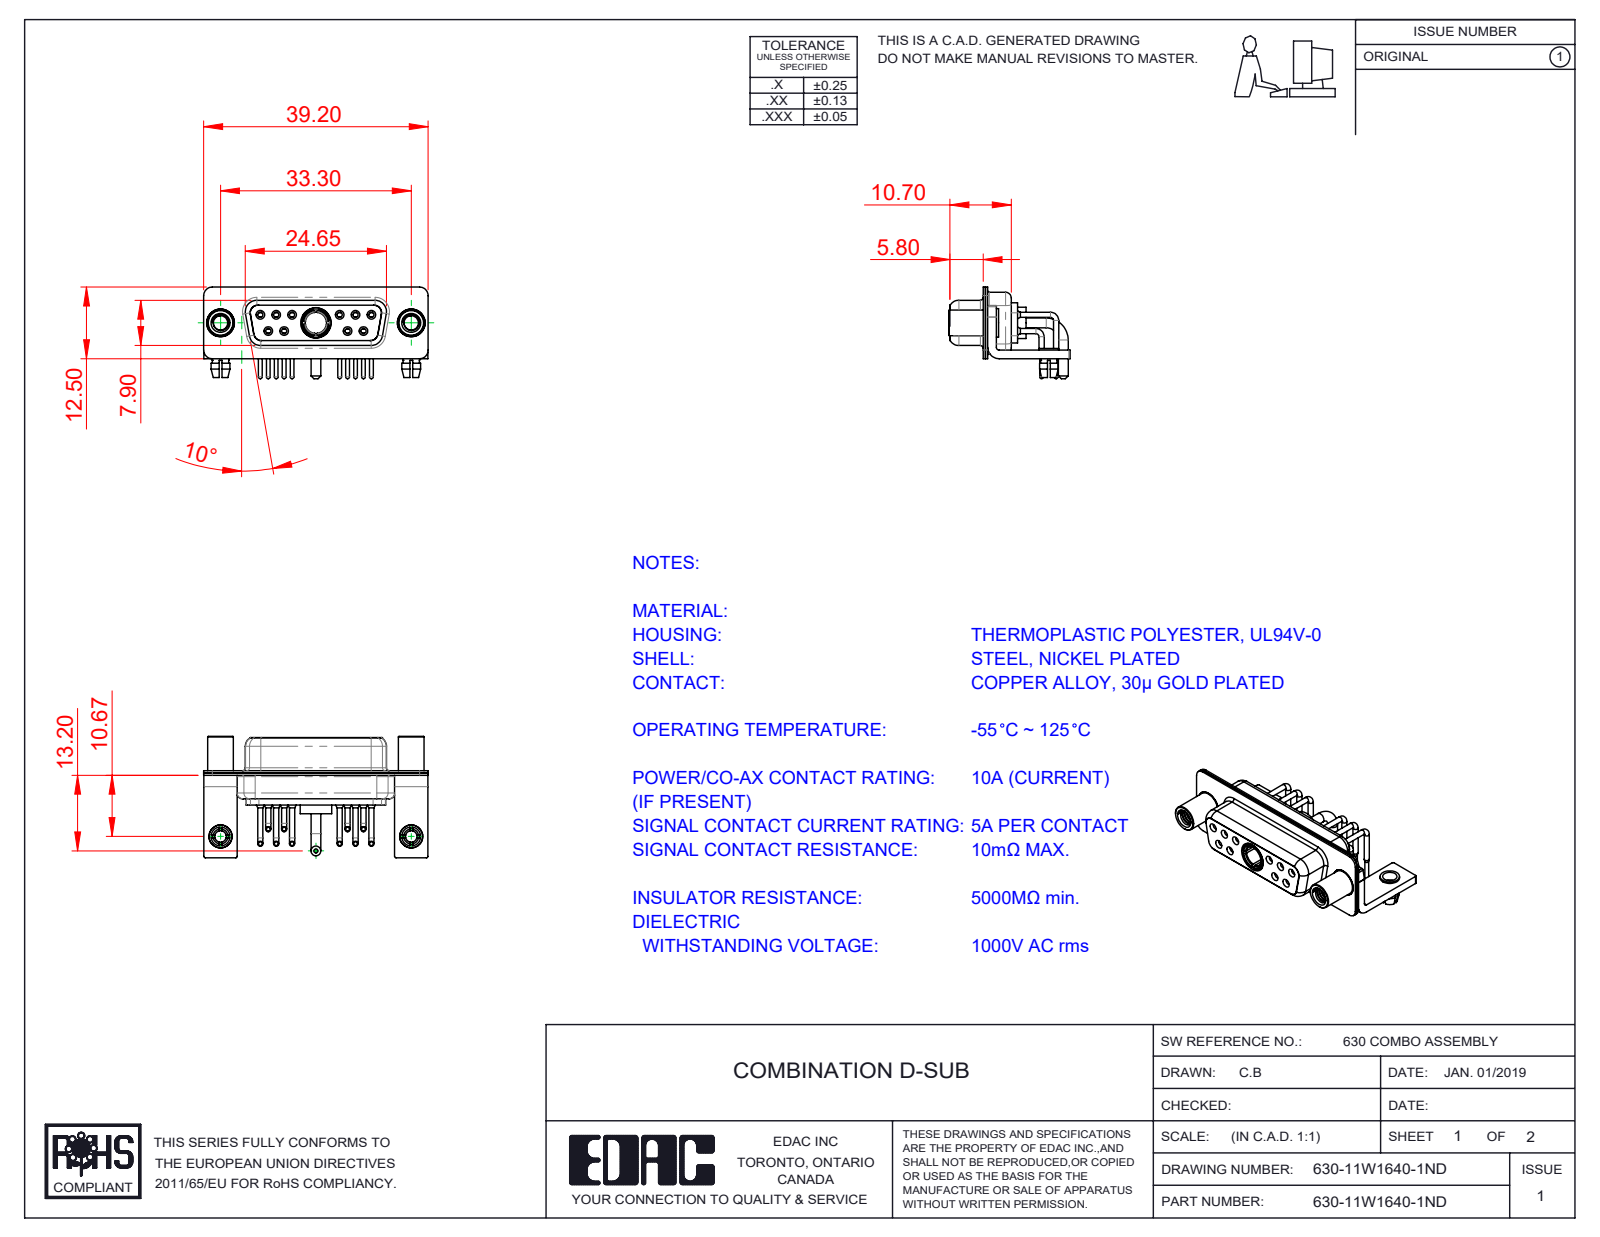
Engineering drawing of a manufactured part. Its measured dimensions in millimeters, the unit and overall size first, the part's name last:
Units: millimetres
Overall size (bounding box): 39.2 × 21.2 × 16
Round holes (diameter × count): ⌀2 ×12, ⌀0.9 ×10, ⌀1.1 ×10, ⌀1.5 ×10, ⌀1.7 ×6, ⌀1.6 ×4, ⌀2.5 ×4, ⌀4.85 ×3, ⌀3.2 ×2, ⌀4 ×2, ⌀4.05 ×2, ⌀3.7 ×1
Round bosses / shafts (diameter × count): ⌀0.9 ×10, ⌀0.65 ×10, ⌀1.6 ×6, ⌀5 ×2, ⌀4.95 ×2, ⌀4.8 ×2, ⌀4.5 ×2, ⌀4 ×2
Partial cylindrical surfaces — rounded edges, fillets, slot ends (radius × count): R0.25 ×16, R1.5 ×16, R2 ×13, R1.35 ×12, R1.6 ×8, R0.5 ×5, R0.6 ×4, R0.65 ×4
Main face-to-face distances: 0.4, 0.8, 0.45, 1.4, 8.45, 1.5, 1.8, 8.9, 6.2, 2.3
Hole centre spacings: 3.16, 2.77, 13.85, 11.08, 16.62, 5.03, 5.04, 5.54
Volume: 3 008 mm³ · Surface area: 7 356 mm²
Bodies: 21 solids, 1077 faces (316 planar, 496 cylindrical, 265 other)
Part name (STEP PRODUCT): 630-11W1640-1ND; 630Combo Contact Row 2; 630Combo Shell Rear_15 Contacts; 630Combo Board Lock (+6 more)
STEP written by: SolidWorks 2020 (CONFIG_CONTROL_DESIGN)
